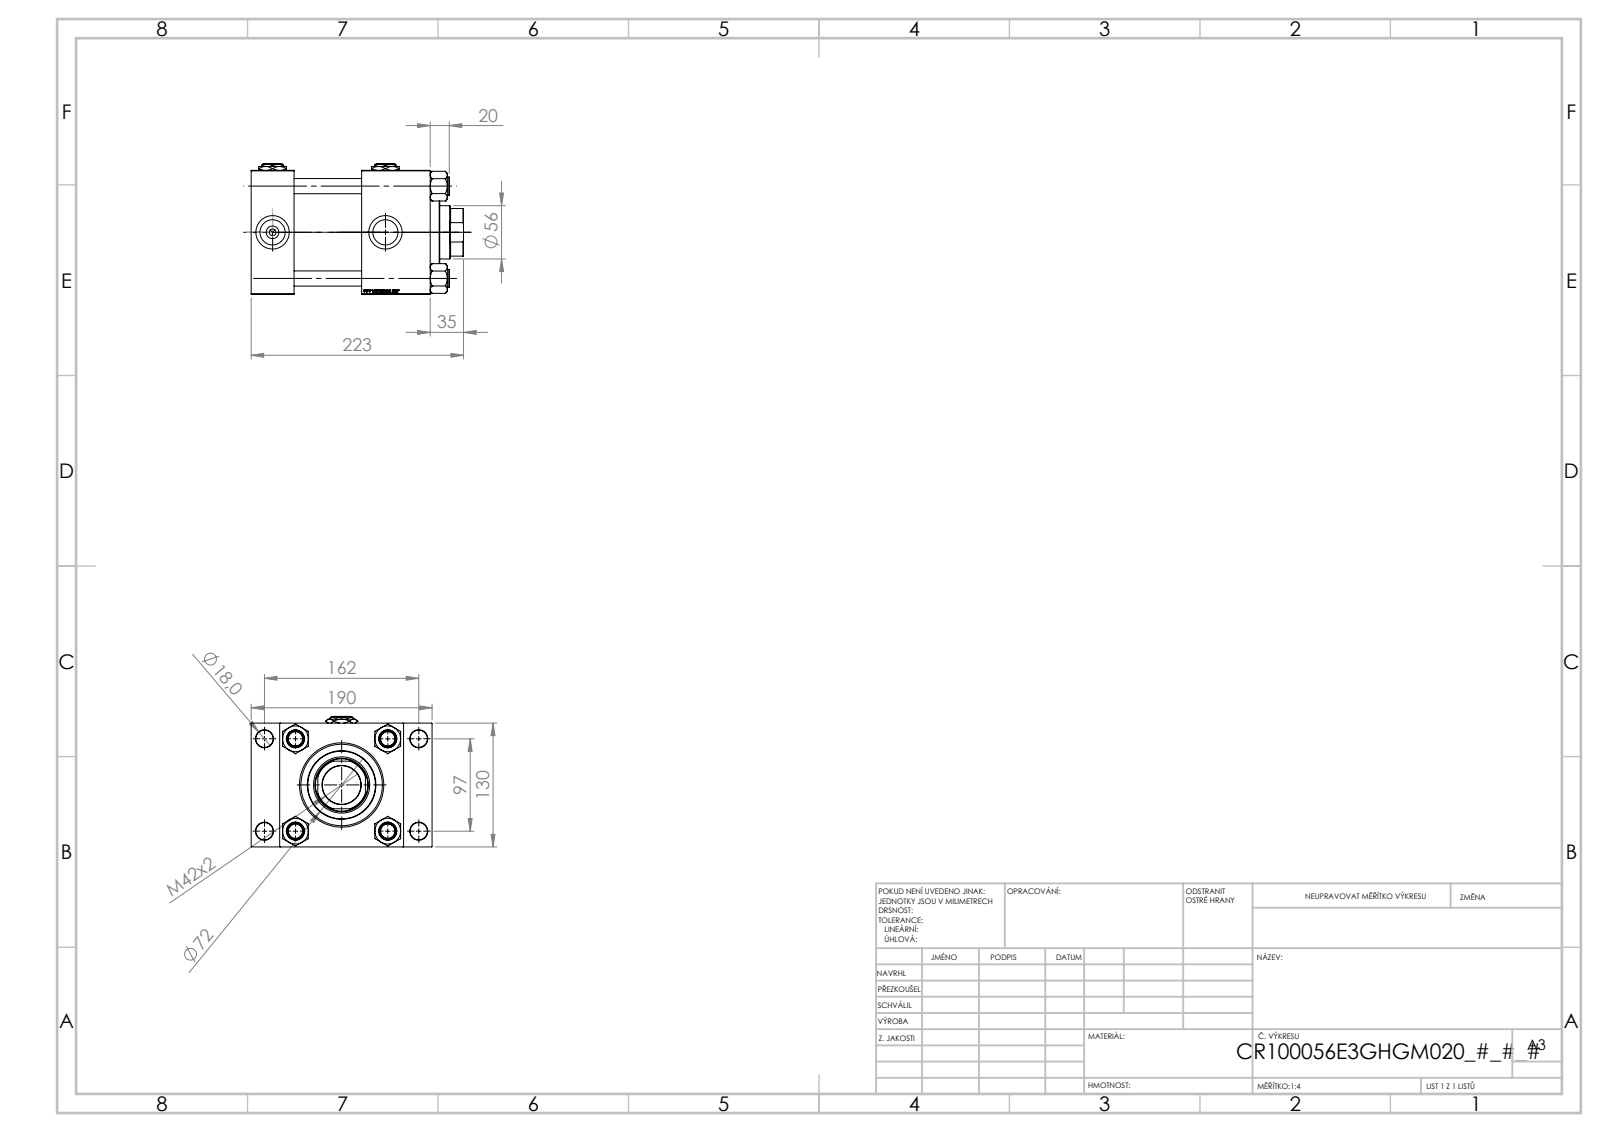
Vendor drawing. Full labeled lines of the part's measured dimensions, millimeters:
Part name (STEP PRODUCT): V215CR_E_Body; V215CR_TYCINKA_E; V215CR_VCP_E; Zatka_pro_OIL_PORT (+2 more)
STEP written by: SolidWorks 2019 (CONFIG_CONTROL_DESIGN)
Units: millimetres
Bodies: 13 solids, 1290 faces (595 planar, 101 cylindrical, 594 other)
Overall size (bounding box): 223 × 190 × 137
Volume: 2 780 000 mm³ · Surface area: 384 372 mm²
Round holes (diameter × count): ⌀16 ×4, ⌀18 ×4, ⌀26.44 ×4, ⌀35 ×4, ⌀7 ×3, ⌀2.5 ×2, ⌀40.5 ×1, ⌀56 ×1, ⌀59 ×1, ⌀76 ×1, ⌀85.5 ×1, ⌀100 ×1
Round bosses / shafts (diameter × count): ⌀19 ×4, ⌀106 ×1, ⌀72 ×1
Partial cylindrical surfaces — rounded edges, fillets, slot ends (radius × count): R27 ×1
Main face-to-face distances: 130, 45, 188, 143, 30, 160, 71, 116, 72, 20
Hole centre spacings: 32.55, 49.02, 62.87, 68.52, 94.41, 96.9, 101.73, 102.27
